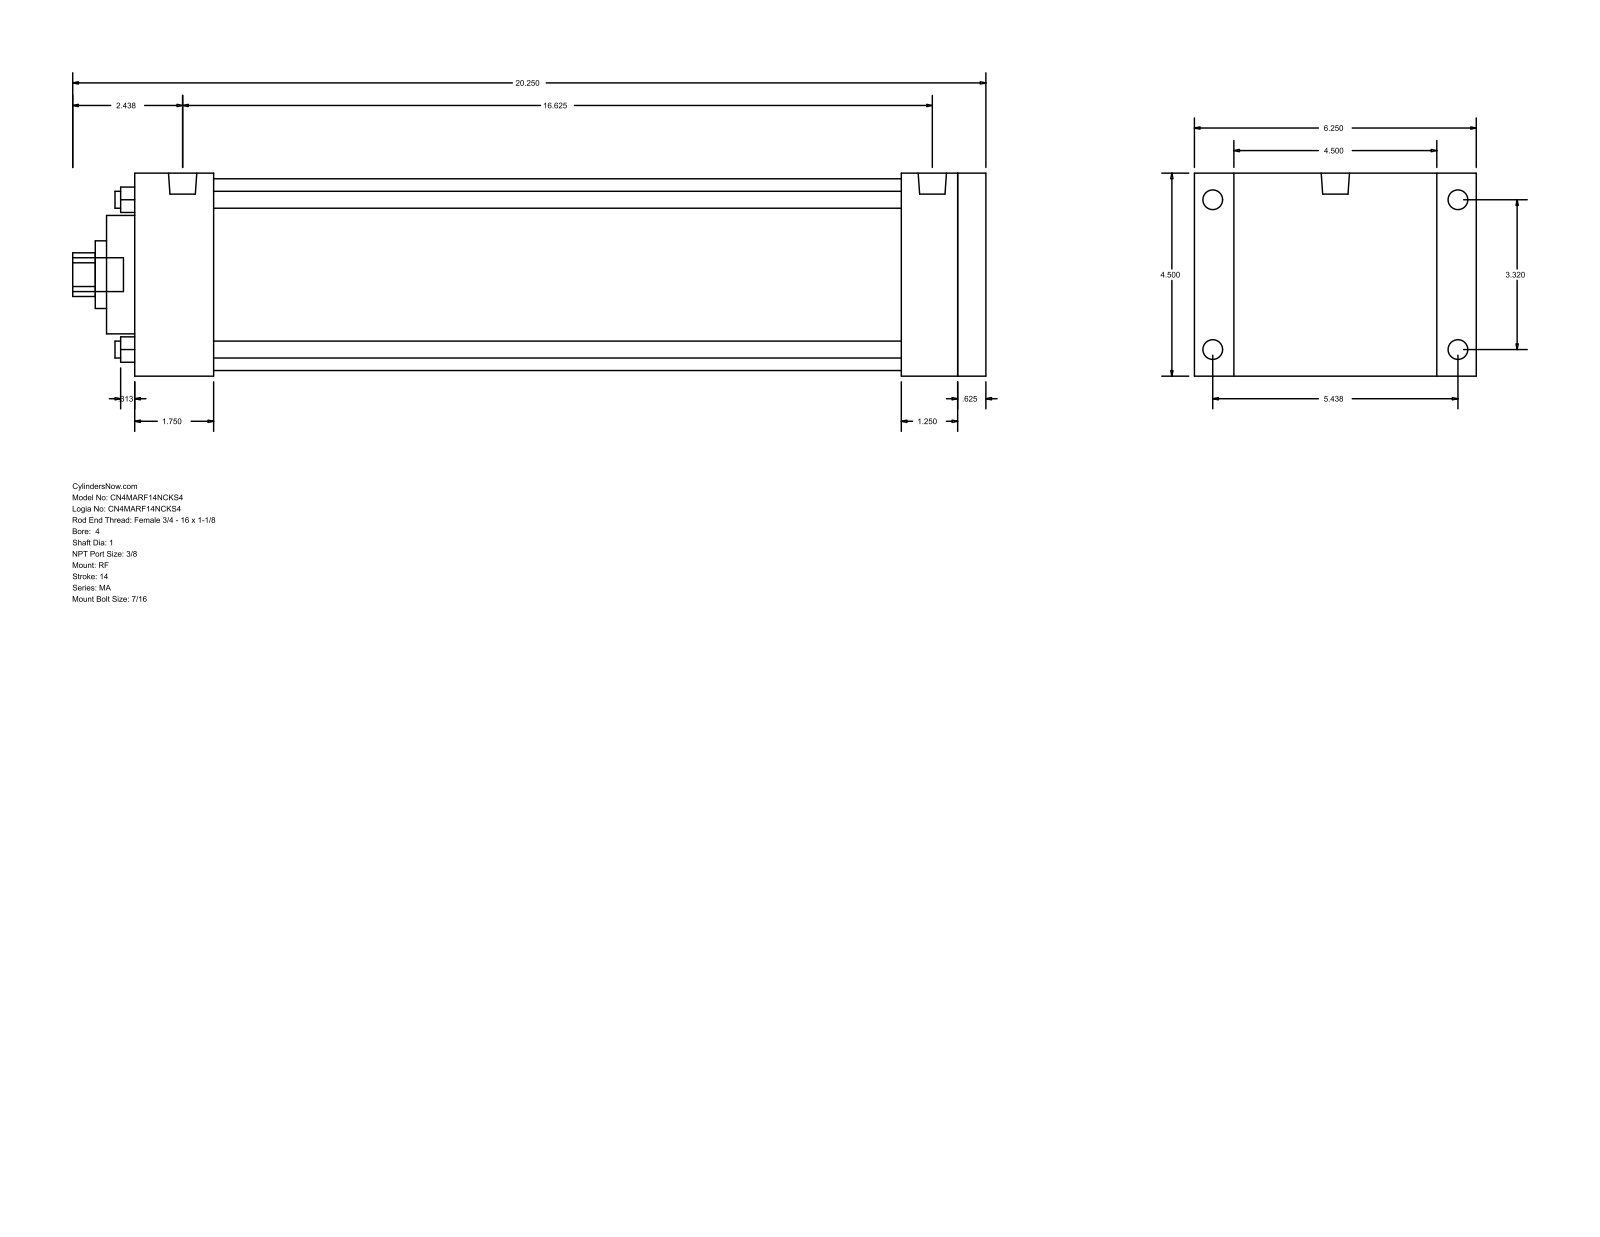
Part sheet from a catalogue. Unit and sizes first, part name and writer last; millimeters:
Units: millimetres
Overall size (bounding box): 514.35 × 158.75 × 114.3
Round holes (diameter × count): ⌀9.53 ×4, ⌀25.4 ×1, ⌀38.1 ×1, ⌀66.67 ×1, ⌀107.95 ×1
Round bosses / shafts (diameter × count): ⌀11.11 ×8, ⌀15.93 ×2, ⌀19.05 ×1
Partial cylindrical surfaces — rounded edges, fillets, slot ends (radius × count): R12.29 ×1
Main face-to-face distances: 114.3, 479.43, 15.87, 463.56, 22.23, 136.53, 431.81, 31.75, 47.62, 44.46
Hole centre spacings: 59.62, 84.32, 119.25
Bodies: 0 solids, 94 faces (65 planar, 29 cylindrical, 0 other)
Part name (STEP PRODUCT): MA_RF__0400_1
STEP written by: GSSL Pune (CONFIG_CONTROL_DESIGN)
